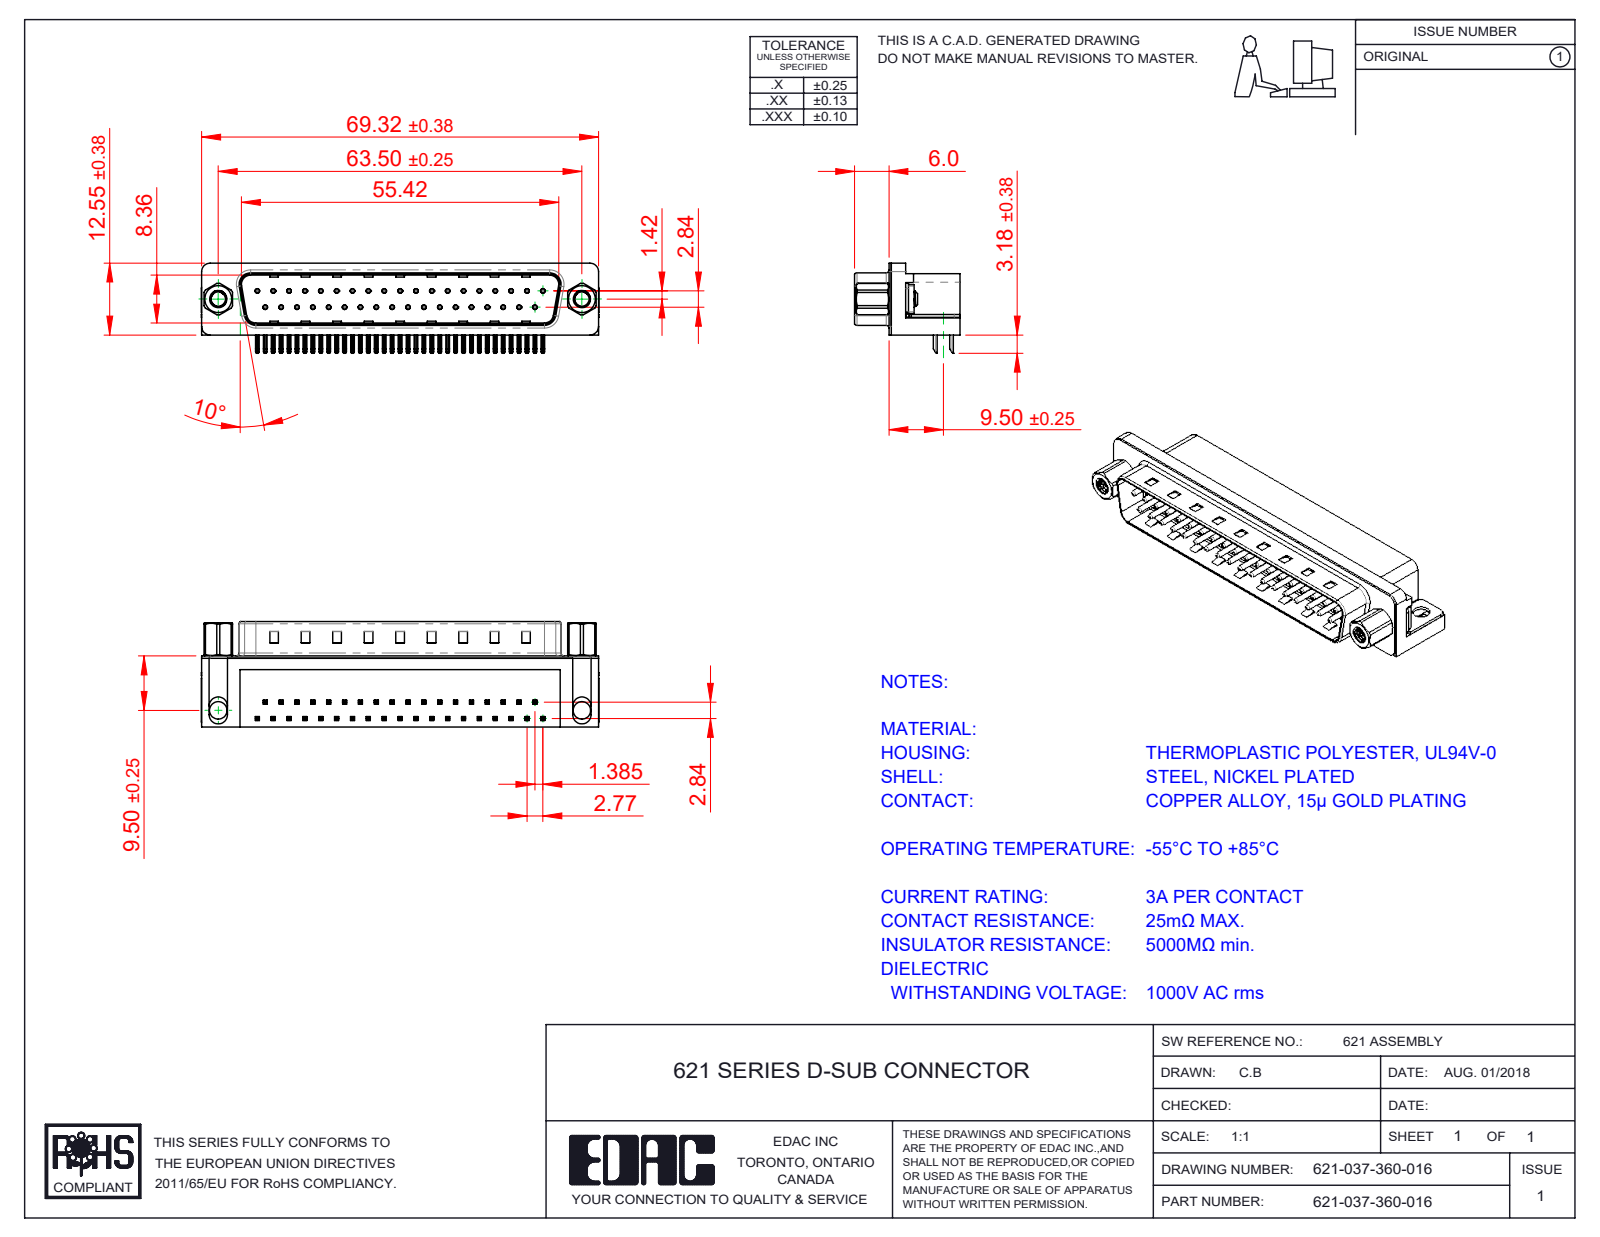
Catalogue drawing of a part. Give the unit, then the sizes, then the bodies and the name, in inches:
Units: inches
Overall size (bounding box): 2.732 × 0.724 × 0.619
Round holes (diameter × count): ⌀0.014 ×37, ⌀0.031 ×37, ⌀0.098 ×2, ⌀0.12 ×2, ⌀0.157 ×2, ⌀0.189 ×2, ⌀0.197 ×2
Round bosses / shafts (diameter × count): ⌀0.03 ×37, ⌀0.193 ×2, ⌀0.187 ×2, ⌀0.154 ×2, ⌀0.118 ×2
Partial cylindrical surfaces — rounded edges, fillets, slot ends (radius × count): R0.01 ×156, R0.005 ×74, R0.039 ×16, R0.02 ×9, R0.063 ×8, R0.059 ×7, R0.035 ×4, R0.079 ×4
Main face-to-face distances: 0.016, 0.472, 0.407, 0.345, 0.083, 0.067, 0.412, 0.428, 0.354, 0.488
Hole centre spacings: 0.124, 0.109, 0.218, 0.327, 0.436, 0.545, 0.763, 0.872
Volume: 0.541 in³ · Surface area: 16.45 in²
Bodies: 45 solids, 3345 faces (2033 planar, 1011 cylindrical, 301 other)
Part name (STEP PRODUCT): 621 M3 Hex Standoff 5; 621-037-360-016; 621 Shell_37 Socket; 621 Thru Hole Board Mount (+4 more)
STEP written by: SolidWorks 2016 (CONFIG_CONTROL_DESIGN)
